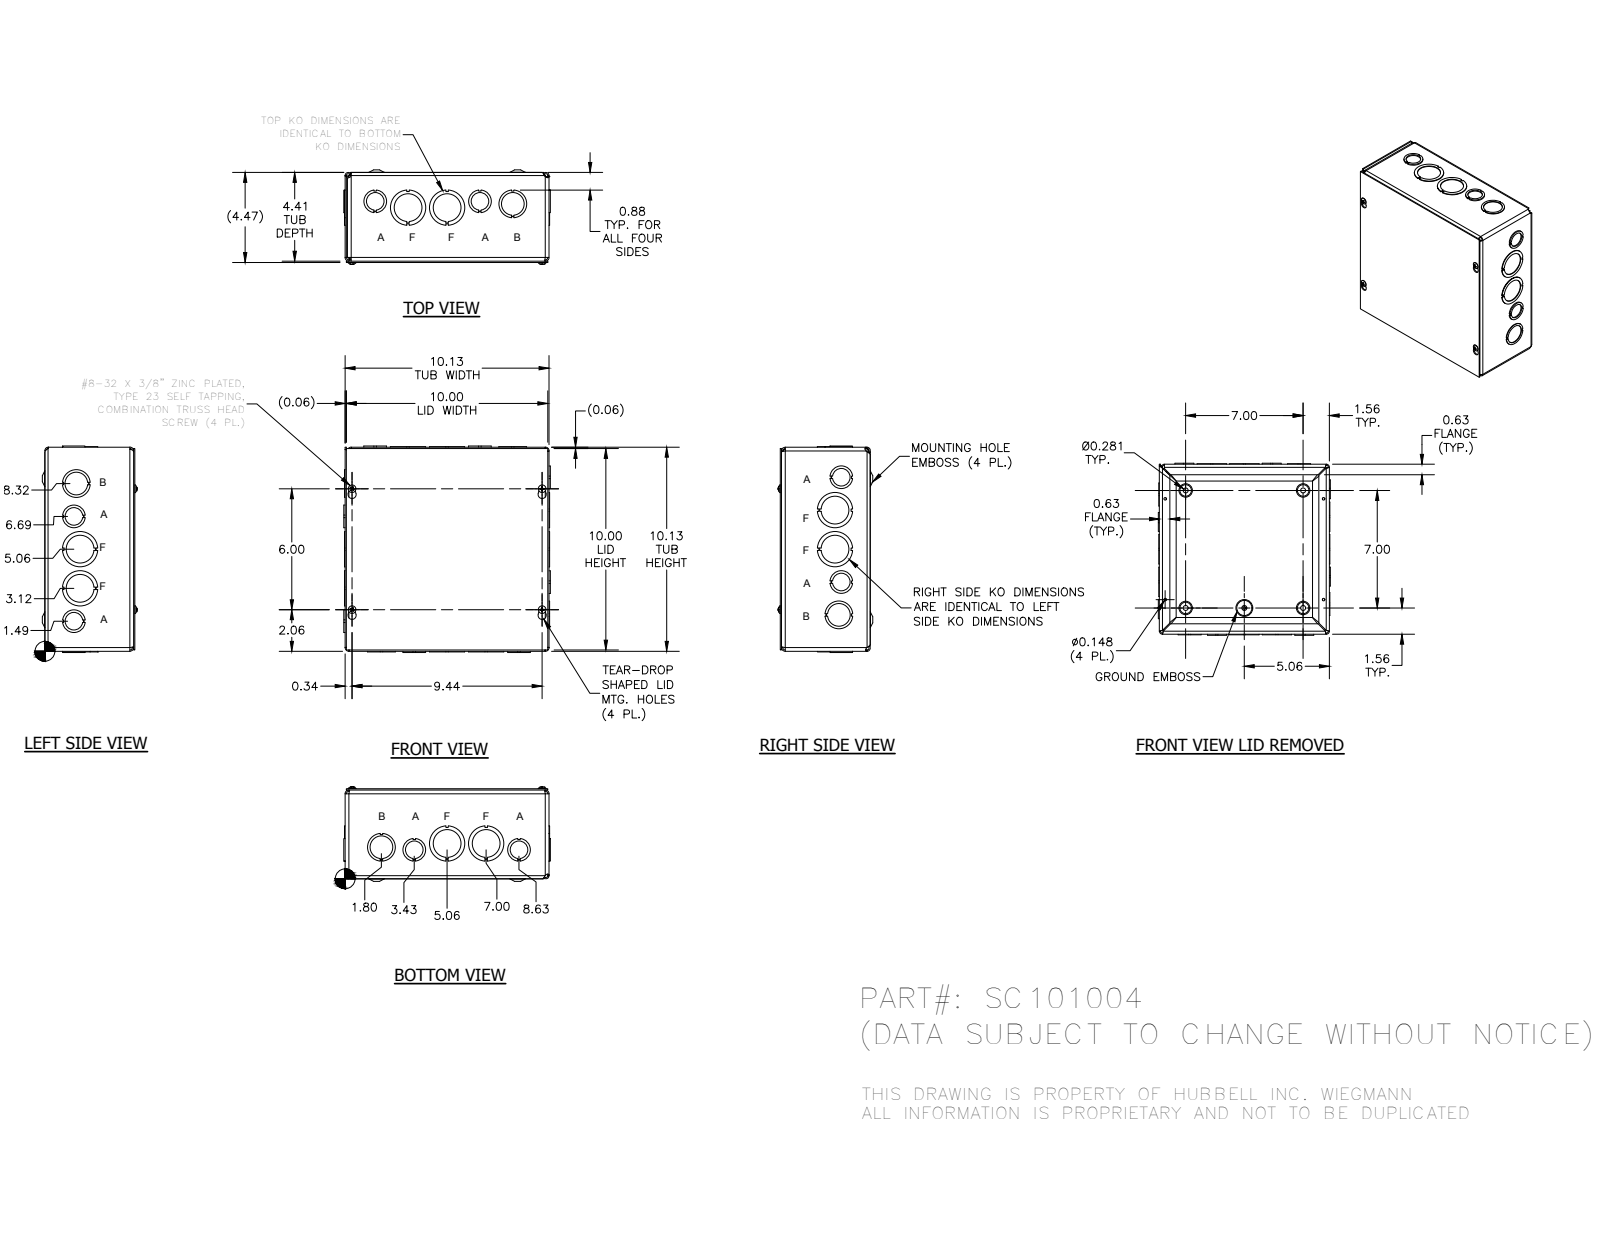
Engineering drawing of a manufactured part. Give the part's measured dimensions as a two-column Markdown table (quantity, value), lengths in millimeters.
| quantity | value |
| --- | --- |
| part name | SC1010BKP; SC101004WRA; SC1010LID; 34056 (+1 more) |
| STEP written by | Autodesk Inventor 2014 (AUTOMOTIVE_DESIGN) |
| units | millimeters |
| bodies | 22 solids, 918 faces (573 planar, 187 cylindrical, 158 other) |
| overall size | 260.32 × 260.32 × 119.2 |
| round holes (diameter × count) | 28.57 × 12, 34.92 × 10, 22.22 × 8, 44.45 × 6, 3.76 × 4, 7.62 × 4, 4.19 × 1 |
| round bosses / shafts (diameter × count) | 9.75 × 4, 4.17 × 4, 5.8 × 1 |
| partial cylindrical surfaces (radius × count) | 3.17 × 12, 4.75 × 8, 1.4 × 4, 1.57 × 4, 2.38 × 4, 2.97 × 4, 3.15 × 4, 3.96 × 4 |
| main face-to-face distances | 1.57, 110.32, 111.89, 1.58, 1.59, 111.91, 113.48, 257.18, 255.6, 255.61 |
| hole center spacings | 42.15, 49.28, 91.03, 33.87, 132.08, 132.17, 167.98, 177.8 |
